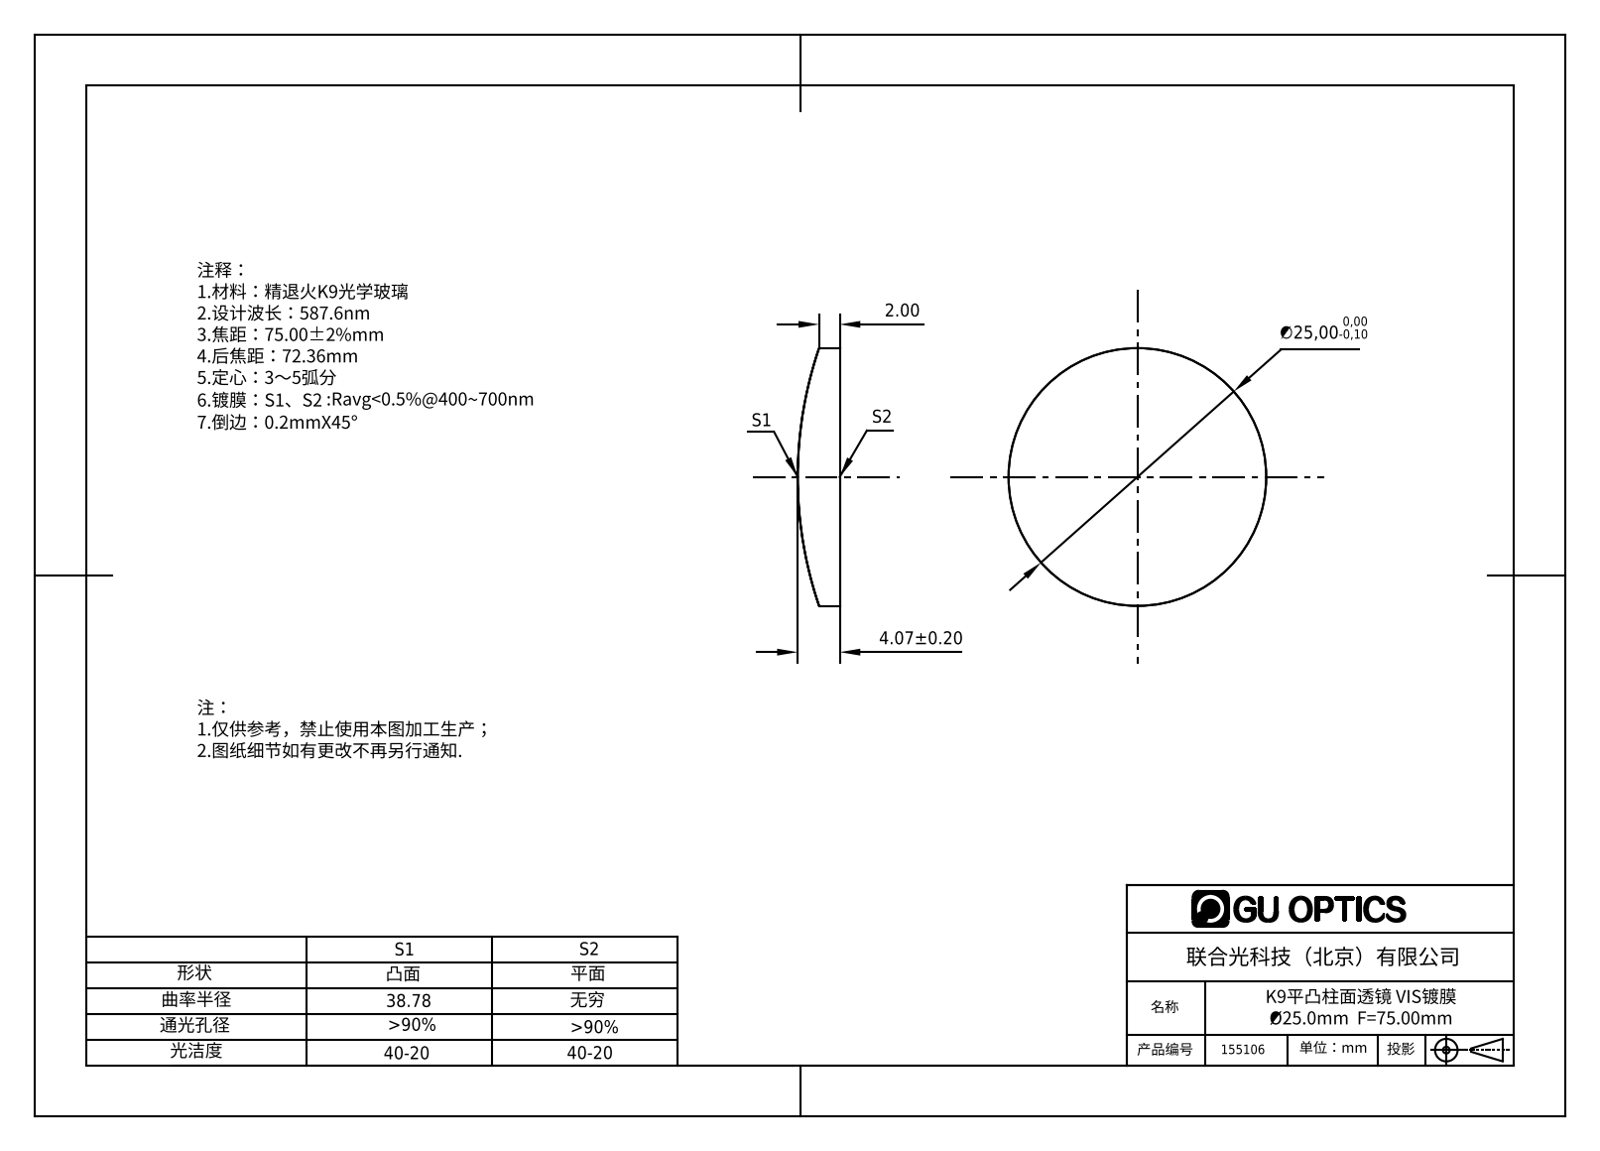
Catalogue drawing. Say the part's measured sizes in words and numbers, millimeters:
The part is named "155040". Its 3-D file was written by "SolidWorks 2016 (AUTOMOTIVE_DESIGN)". It is 1 solid with 4 faces: 1 planar, 3 cylindrical and 0 other. Overall it measures 25 by 25 by 4.07 millimeters. Its volume is 1 747 cubic millimeters and its surface area 1 227 square millimeters. Round bosses or shafts: 1 of diameter 25. Partial cylindrical surfaces (rounded edges, fillets, slot ends): 1 of radius 38.78.
